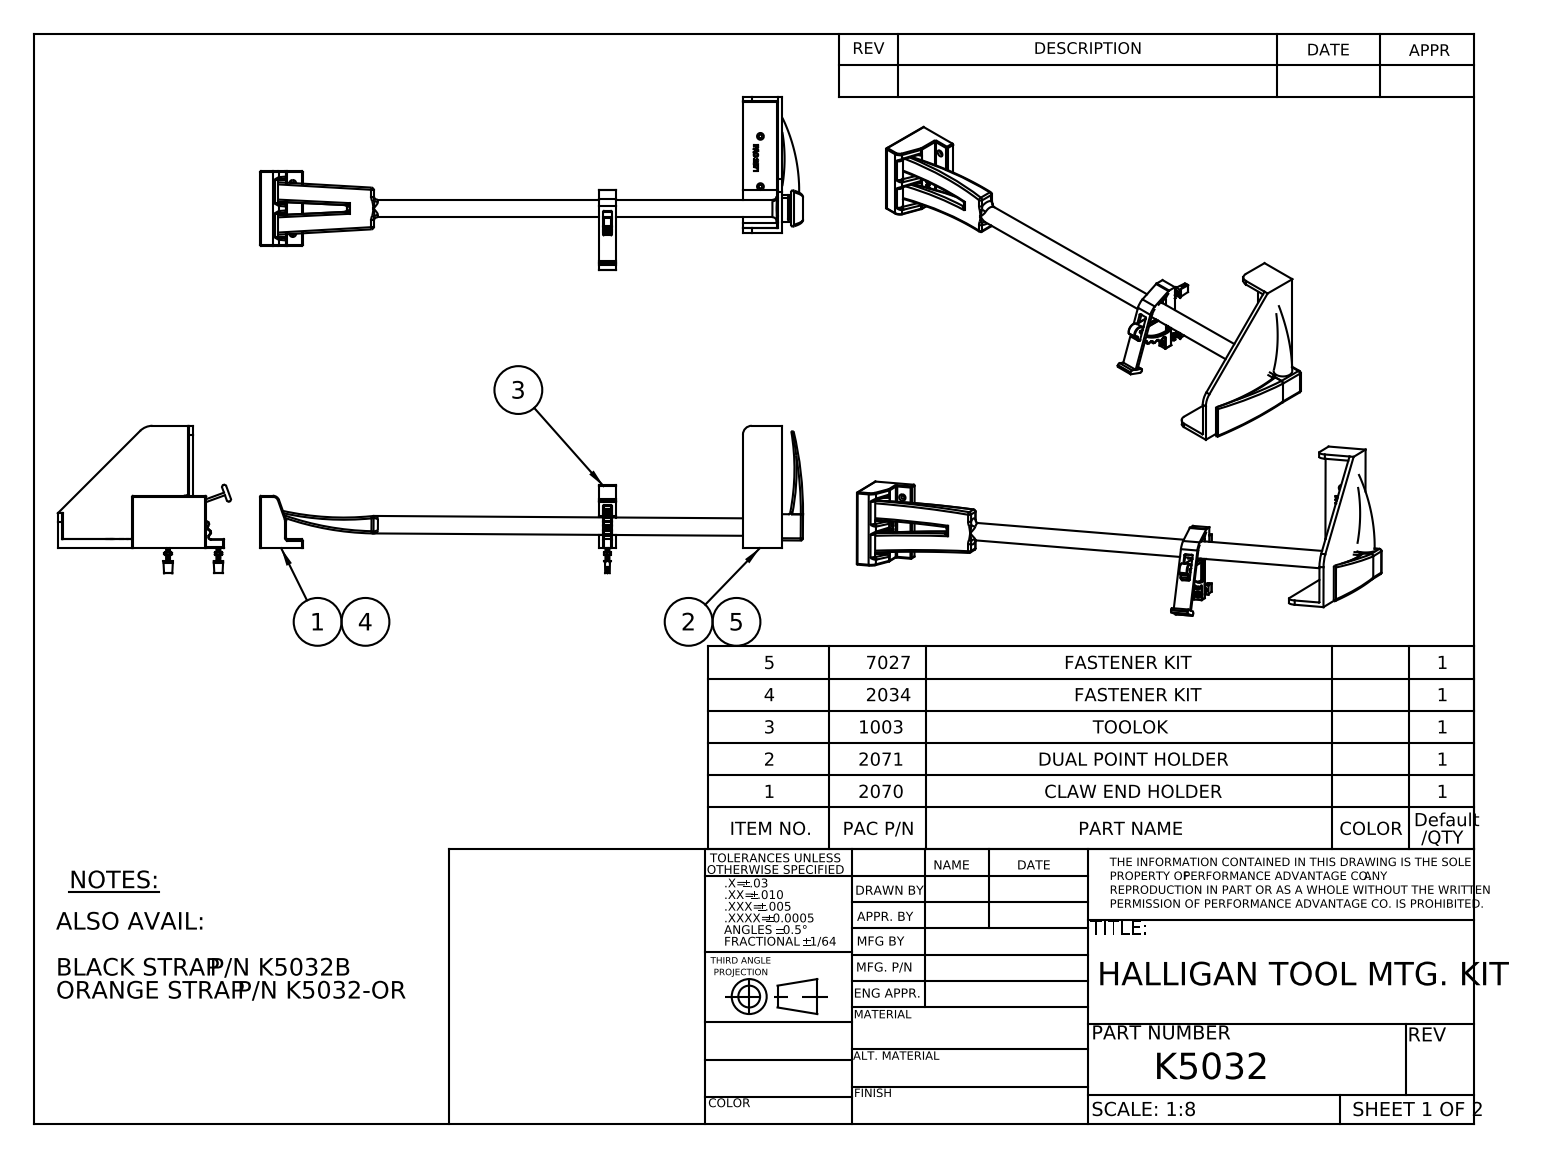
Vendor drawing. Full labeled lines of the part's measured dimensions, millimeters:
Part name (STEP PRODUCT): haliigan; K5032; 2059_#10; 2044_82DEG 10-32x1.25 18-8 SS (+7 more)
STEP written by: SolidWorks 2010 (CONFIG_CONTROL_DESIGN)
Units: millimetres
Bodies: 11 solids, 1283 faces (401 planar, 502 cylindrical, 380 other)
Overall size (bounding box): 757.8 × 251.6 × 214.3
Volume: 1 266 000 mm³ · Surface area: 258 600 mm²
Round holes (diameter × count): ⌀5.1 ×6, ⌀5.1 ×1
Round bosses / shafts (diameter × count): ⌀4.8 ×2, ⌀3.8 ×2, ⌀25.4 ×1
Partial cylindrical surfaces — rounded edges, fillets, slot ends (radius × count): R0.8 ×42, R3.2 ×31, R1.6 ×14, R1.6 ×10, R3.3 ×8, R0.8 ×6, R7.9 ×6, R0.4 ×4
Main face-to-face distances: 6.4, 12.7, 751.5, 757.8, 190.5, 9.5, 57.2, 50.8, 38.1, 241.3
Hole centre spacings: 73, 73, 224.3, 245, 245, 283.6, 457.5, 457.5
